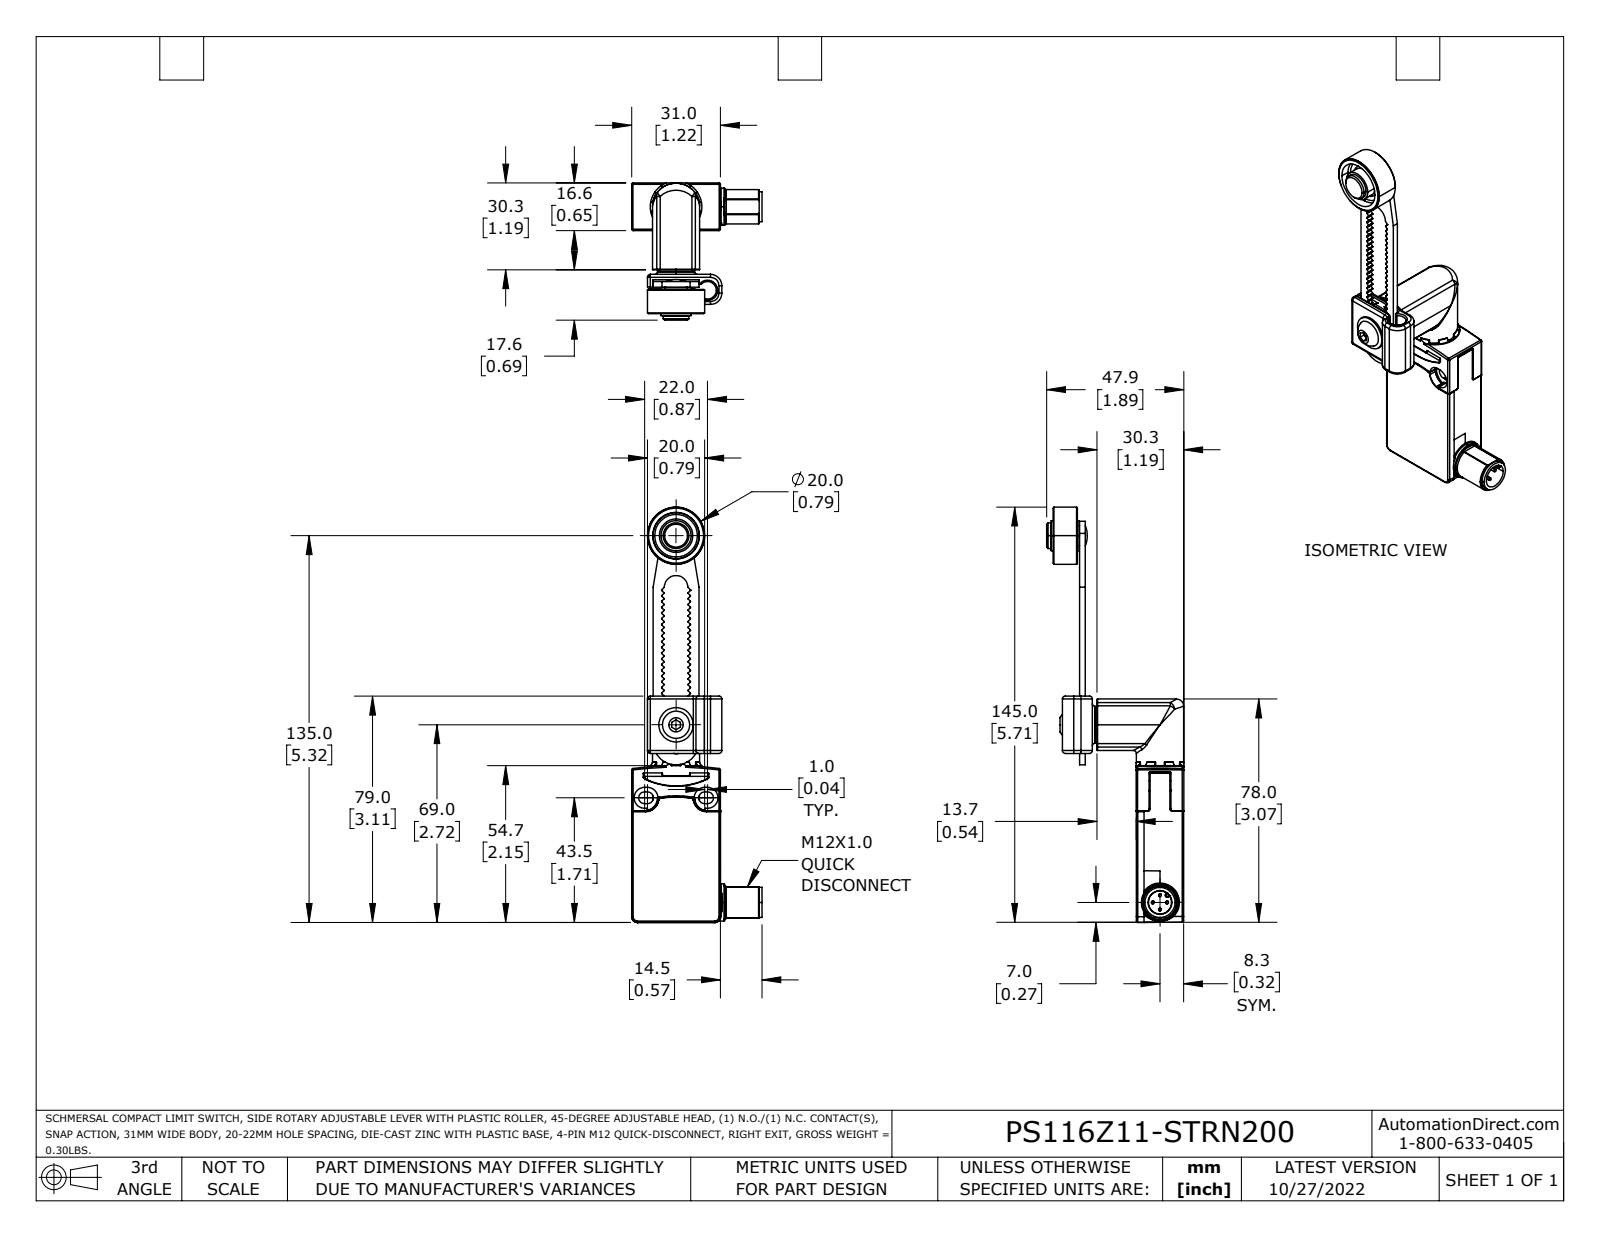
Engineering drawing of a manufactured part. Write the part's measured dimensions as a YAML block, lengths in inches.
part_name: "PS116Z11-STRN200_Default"
step_written_by: "SolidWorks 2021 (CONFIG_CONTROL_DESIGN)"
units: inches
bodies: {solids: 1, faces: 1431, planar: 446, cylindrical: 686, other: 299}
overall_size: [5.71, 1.886, 1.791]
volume: 2.583
surface_area: 32.08
round_holes:
  - {diameter: 0.079, count: 1}
  - {diameter: 0.24, count: 1}
  - {diameter: 0.315, count: 1}
  - {diameter: 0.327, count: 1}
  - {diameter: 0.48, count: 1}
  - {diameter: 0.571, count: 1}
  - {diameter: 0.583, count: 1}
round_bosses_or_shafts:
  - {diameter: 0.039, count: 4}
  - {diameter: 0.512, count: 2}
  - {diameter: 0.413, count: 2}
  - {diameter: 0.787, count: 1}
  - {diameter: 0.65, count: 1}
  - {diameter: 0.567, count: 1}
  - {diameter: 0.524, count: 1}
  - {diameter: 0.475, count: 1}
partial_cylinders:
  - {radius: 0.008, count: 229}
  - {radius: 0.004, count: 67}
  - {radius: 0.02, count: 41}
  - {radius: 0.039, count: 27}
  - {radius: 0.079, count: 12}
  - {radius: 0.014, count: 10}
  - {radius: 0.118, count: 5}
  - {radius: 0.081, count: 4}
face_to_face_distances: [0.65, 0.781, 0.079, 1.431, 1.352, 0.703, 0.652, 0.201, 0.098, 0.177]
hole_center_spacings: [1.227, 1.615, 2.598]
